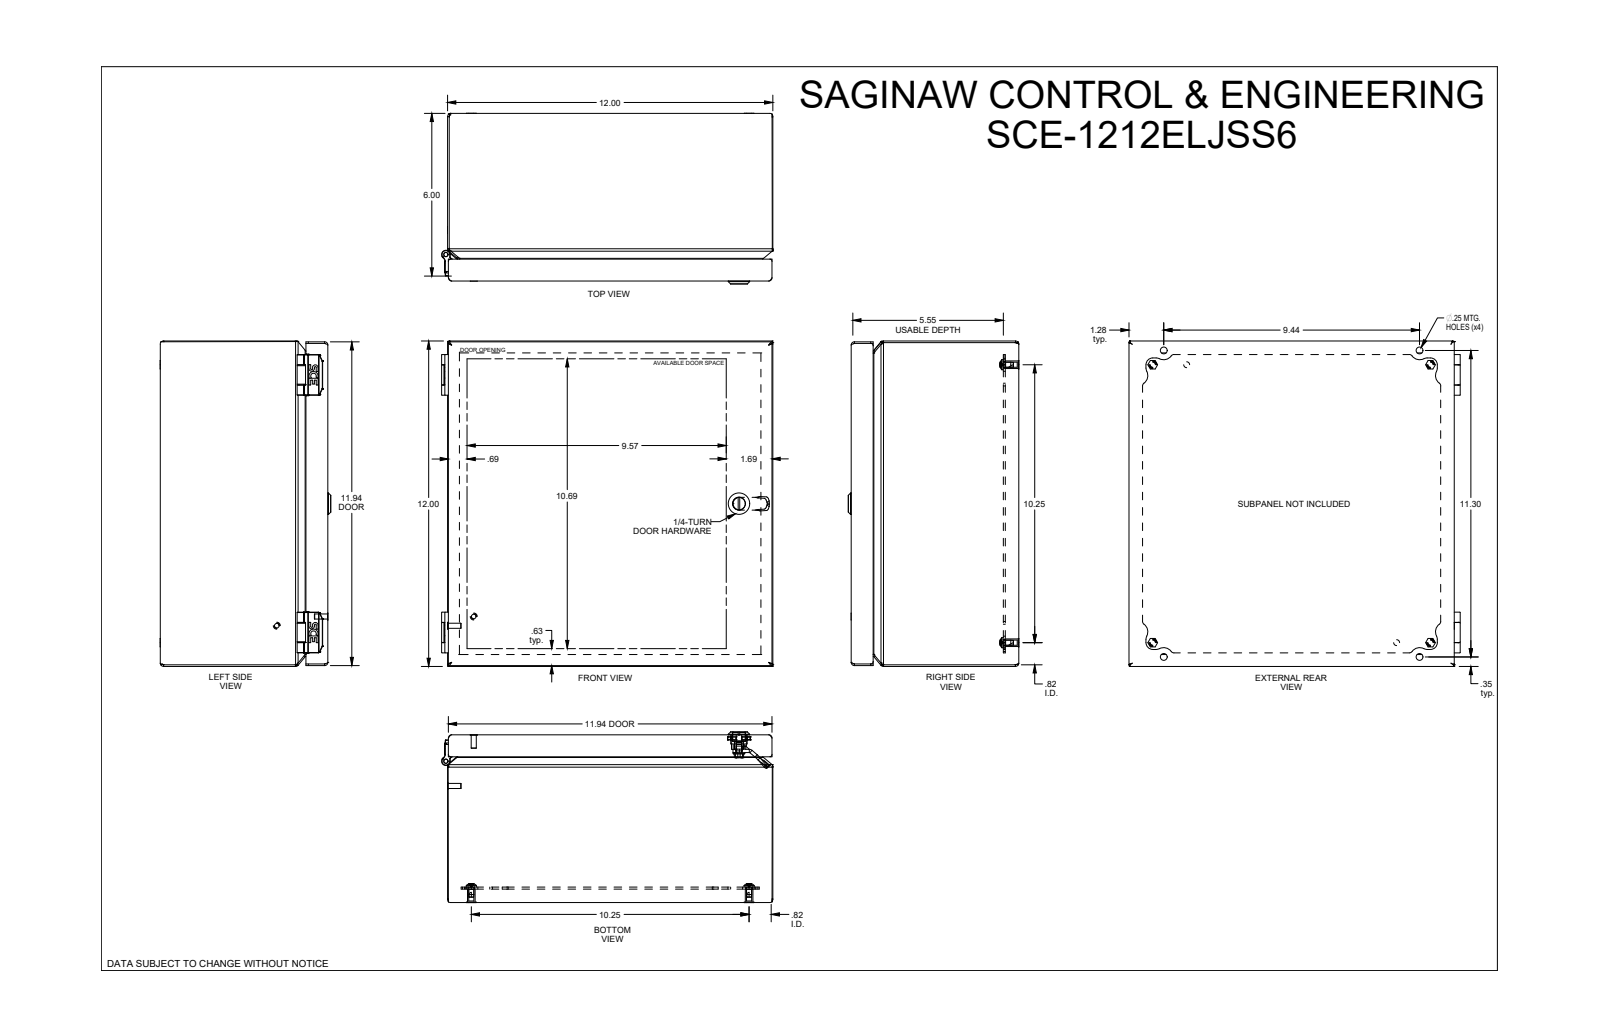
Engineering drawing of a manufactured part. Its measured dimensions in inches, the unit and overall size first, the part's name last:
Units: inches
Overall size (bounding box): 12.19 × 12.06 × 6.296
Round holes (diameter × count): ⌀0.19 ×4, ⌀0.25 ×4, ⌀0.284 ×4, ⌀0.02 ×2, ⌀0.1 ×2, ⌀0.218 ×2, ⌀0.266 ×2, ⌀0.158 ×1, ⌀0.196 ×1, ⌀0.2 ×1, ⌀0.239 ×1, ⌀0.254 ×1
Round bosses / shafts (diameter × count): ⌀0.188 ×6, ⌀0.373 ×4, ⌀0.28 ×4, ⌀0.16 ×4, ⌀0.26 ×2, ⌀0.256 ×2, ⌀0.237 ×2, ⌀0.23 ×2
Partial cylindrical surfaces — rounded edges, fillets, slot ends (radius × count): R0.03 ×28, R0.013 ×21, R0.05 ×16, R0.25 ×13, R0.125 ×11, R0.01 ×10, R0.06 ×10, R0.344 ×8
Main face-to-face distances: 0.059, 12.001, 0.06, 6.125, 6.066, 6.185, 6.126, 12.06, 5.614, 0.075
Hole centre spacings: 10.25, 10.31, 0.06, 1.25, 5.138, 9, 10.25, 10.251
Volume: 49.3 in³ · Surface area: 1 549 in²
Bodies: 30 solids, 947 faces (363 planar, 316 cylindrical, 268 other)
Part name (STEP PRODUCT): SCE-1212ELJ
STEP written by: SolidWorks 2019 (AUTOMOTIVE_DESIGN)
